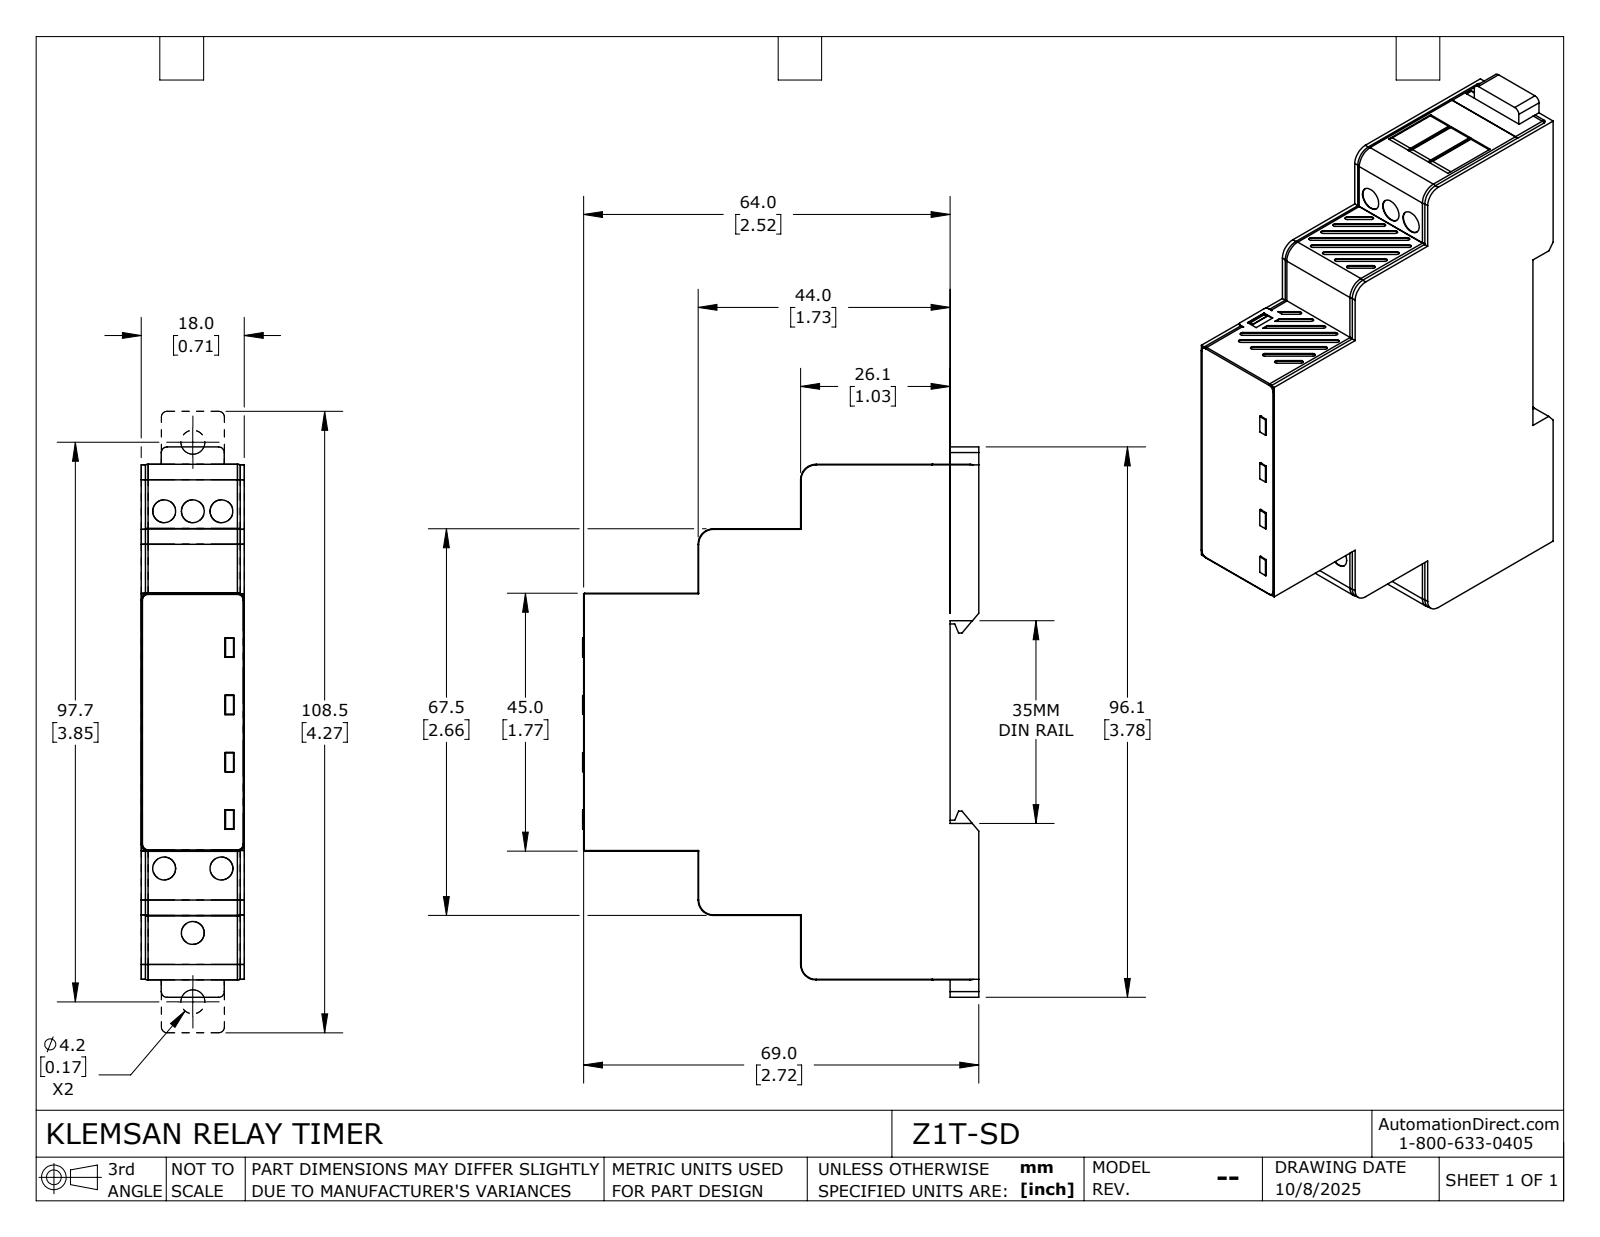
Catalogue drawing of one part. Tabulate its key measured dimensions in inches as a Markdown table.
| quantity | value |
| --- | --- |
| part name | Z1T-SD |
| STEP written by | SolidWorks 2024 (CONFIG_CONTROL_DESIGN) |
| units | inches |
| bodies | 3 solids, 440 faces (280 planar, 60 cylindrical, 100 other) |
| overall size | 3.782 × 2.722 × 0.709 |
| volume | 5.117 in³ |
| surface area | 27.72 in² |
| round holes (diameter × count) | 0.165 × 2, 0.157 × 1 |
| partial cylindrical surfaces (radius × count) | 0.047 × 16, 0.008 × 4, 0.039 × 4, 0.102 × 4, 0.106 × 4, 0.02 × 2, 0.059 × 2 |
| main face-to-face distances | 0.709, 0.138, 0.571, 0.443, 2.52, 0.197, 2.717, 0.886, 2.654, 2.657 |
| hole center spacings | 0.23, 3.127, 3.357 |
